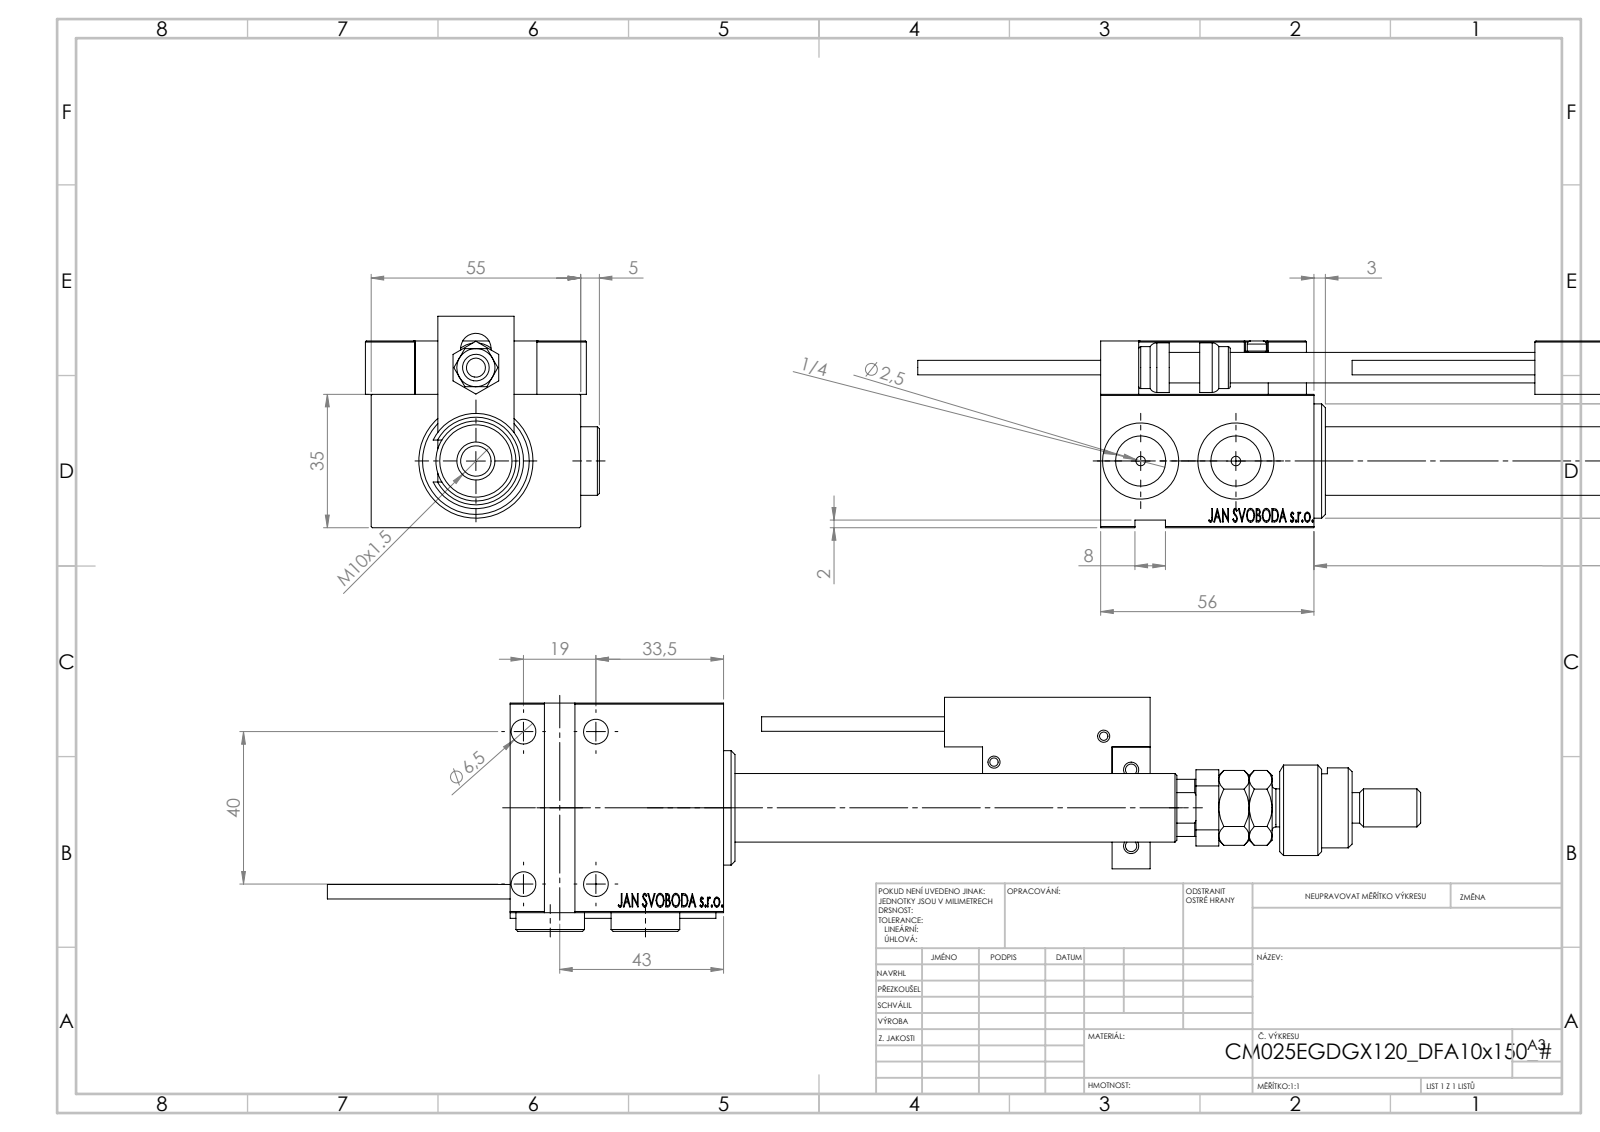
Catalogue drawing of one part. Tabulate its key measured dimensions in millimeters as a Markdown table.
| quantity | value |
| --- | --- |
| part name | SWITCH_X_FRONT_BACK; SWITCH DIM B,W; V450CM_E_VCP; ZARAZKA (+8 more) |
| STEP written by | SolidWorks 2019 (CONFIG_CONTROL_DESIGN) |
| units | millimeters |
| bodies | 28 solids, 1425 faces (629 planar, 207 cylindrical, 589 other) |
| overall size | 287 × 61.4 × 55.5 |
| volume | 190 253 mm³ |
| surface area | 71 395 mm² |
| round holes (diameter × count) | 8 × 6, 3.2 × 4, 4 × 4, 6.5 × 4, 2.5 × 2, 5 × 2, 10.5 × 2, 13.16 × 2, 20 × 2, 7 × 1, 8.5 × 1, 14.5 × 1 |
| round bosses / shafts (diameter × count) | 18 × 2, 5 × 2, 3.8 × 2, 30 × 1, 27 × 1, 25 × 1, 21 × 1, 16 × 1 |
| partial cylindrical surfaces (radius × count) | 0.3 × 30, 3 × 2, 5.25 × 2, 5.5 × 1, 8.5 × 1, 8.75 × 1 |
| main face-to-face distances | 35, 49, 14, 5, 1.5, 56.5, 56, 10, 20, 6 |
| hole center spacings | 20.16, 10.11, 11.37, 19, 20, 29.59, 29.69, 30.04 |
